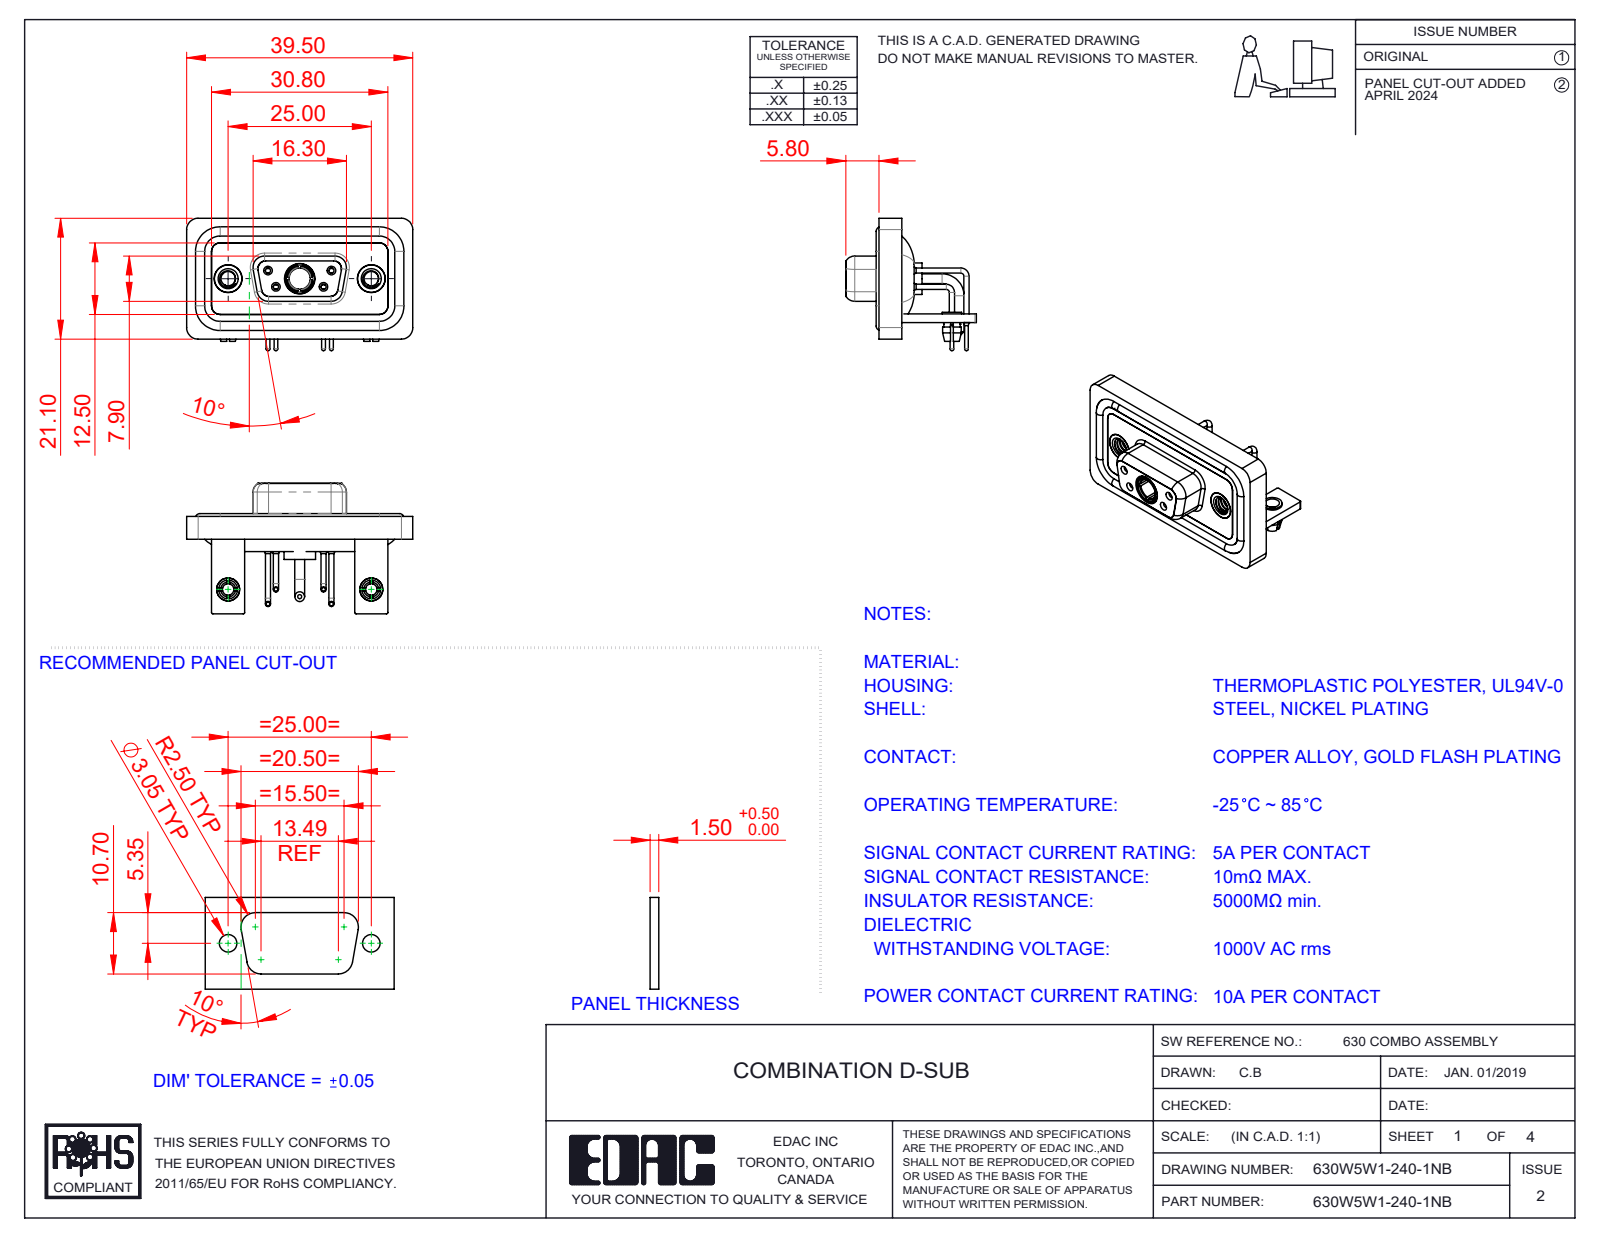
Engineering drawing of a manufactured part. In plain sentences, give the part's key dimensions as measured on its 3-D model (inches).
The part is named "630Combo Board Lock_50 Contacts; 630Combo Housing_5W1; Power Socket_10A RA; 630Combo Threaded Rivet_A (+7 more)". Its 3-D file was written by "SolidWorks 2023 (CONFIG_CONTROL_DESIGN)". It is 17 solids with 810 faces: 262 planar, 359 cylindrical and 189 other. Overall it measures 1.555 by 0.91 by 0.898 inches. Its volume is 0.315 cubic inches and its surface area 13.55 square inches. Round holes: 6 of diameter 0.079, 4 of diameter 0.035, 4 of diameter 0.043, 4 of diameter 0.059, 4 of diameter 0.098, 3 of diameter 0.191, 2 of diameter 0.063, 2 of diameter 0.067, 2 of diameter 0.126, 2 of diameter 0.157, 2 of diameter 0.159, 2 of diameter 0.197. Round bosses or shafts: 6 of diameter 0.063, 4 of diameter 0.035, 4 of diameter 0.026, 2 of diameter 0.195, 2 of diameter 0.189, 2 of diameter 0.157, 2 of diameter 0.134, 2 of diameter 0.13. Partial cylindrical surfaces (rounded edges, fillets, slot ends): 19 of radius 0.079, 18 of radius 0.059, 16 of radius 0.01, 8 of radius 0.053, 8 of radius 0.063, 5 of radius 0.02, 4 of radius 0.024, 4 of radius 0.026. The main face-to-face distances are 0.016, 0.114, 0.059, 0.071, 0.043, 0.146, 0.063, 0.031, 0.098, 0.122. The hole center spacings are 0.124, 0.225, 0.28, 0.492, 0.713, 0.984, 0.173, 0.173.
